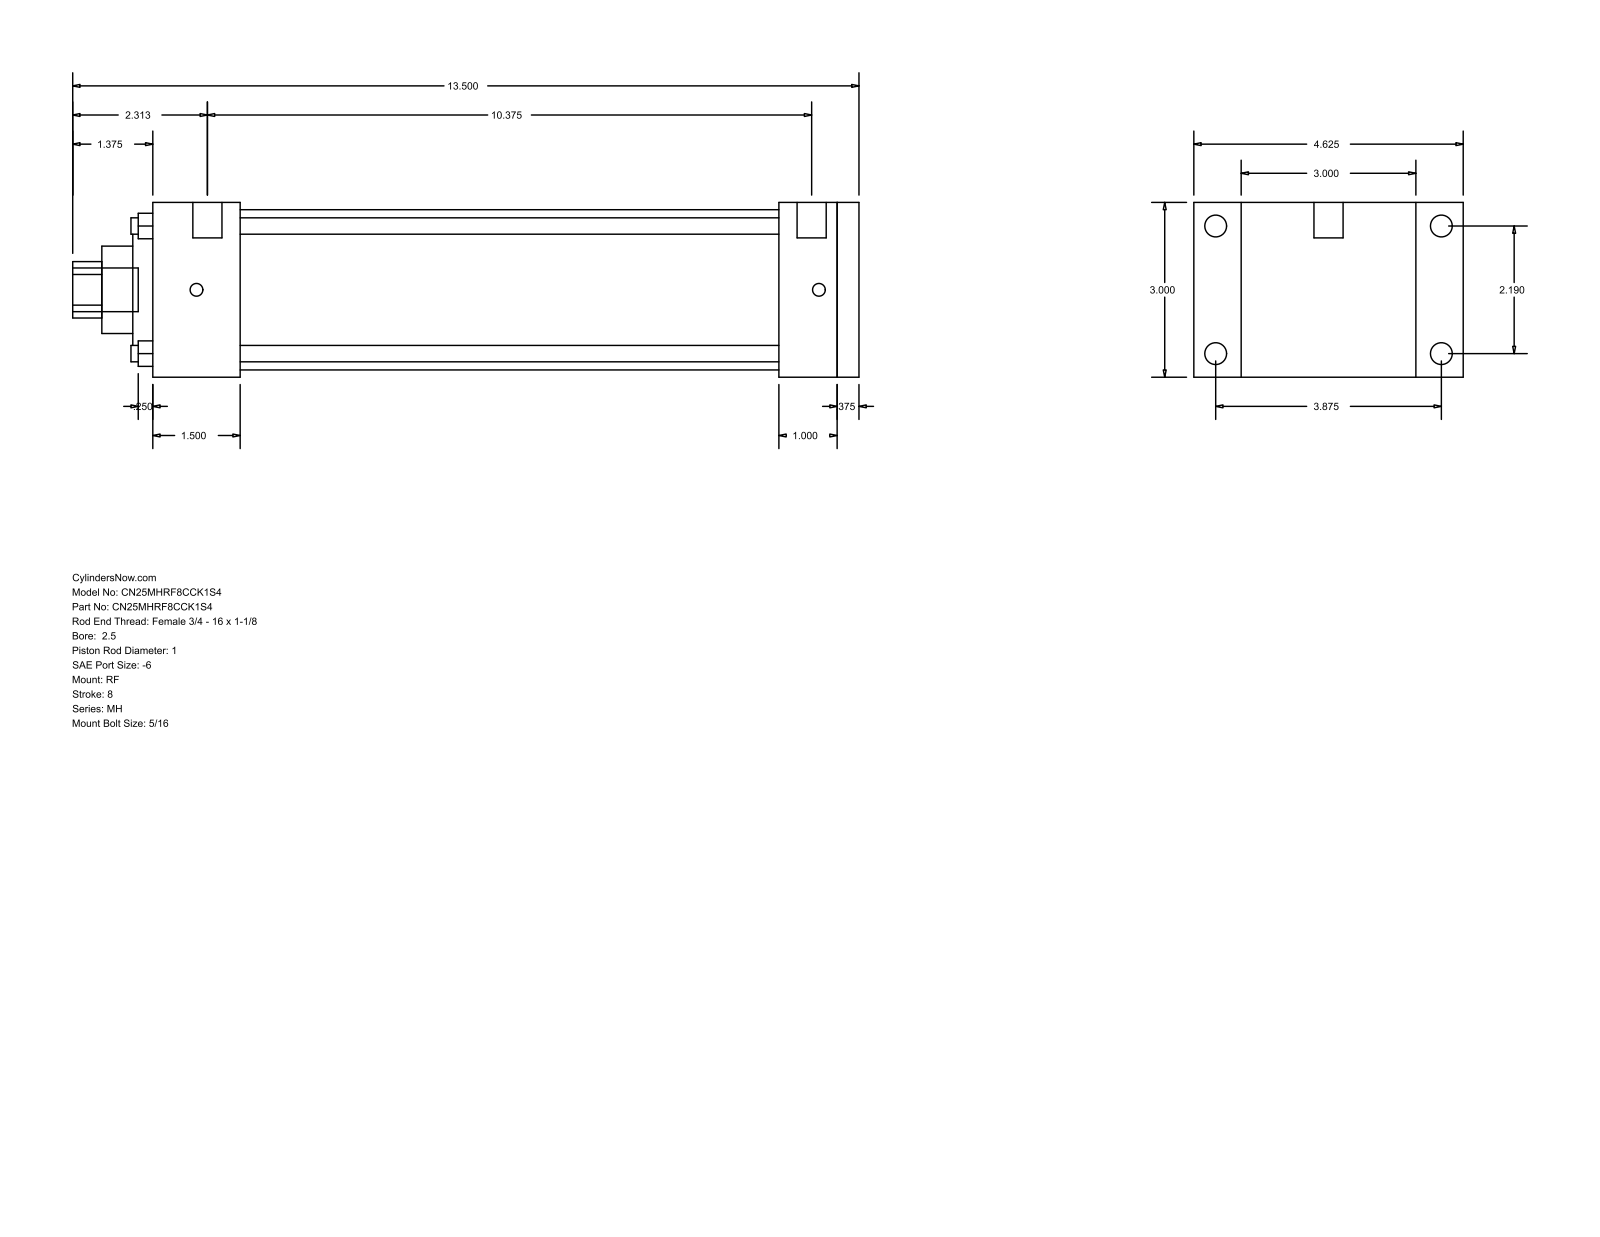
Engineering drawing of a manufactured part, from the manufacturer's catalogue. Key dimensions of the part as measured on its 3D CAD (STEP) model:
Part name (STEP PRODUCT): MH_RF__0250_1
STEP written by: GSSL Pune (CONFIG_CONTROL_DESIGN)
Units: millimetres
Bodies: 0 solids, 94 faces (65 planar, 29 cylindrical, 0 other)
Overall size (bounding box): 342.9 × 117.47 × 76.2
Round holes (diameter × count): ⌀7.14 ×4, ⌀25.4 ×1, ⌀38.1 ×1, ⌀60.33 ×1, ⌀69.85 ×1
Round bosses / shafts (diameter × count): ⌀9.53 ×4, ⌀5.56 ×4, ⌀12.7 ×2, ⌀19.05 ×1
Partial cylindrical surfaces — rounded edges, fillets, slot ends (radius × count): R12.29 ×1
Main face-to-face distances: 76.2, 9.52, 307.98, 298.46, 25.4, 34.92, 273.06, 38.11, 234.95, 260.35
Hole centre spacings: 39.33, 55.62, 78.66
